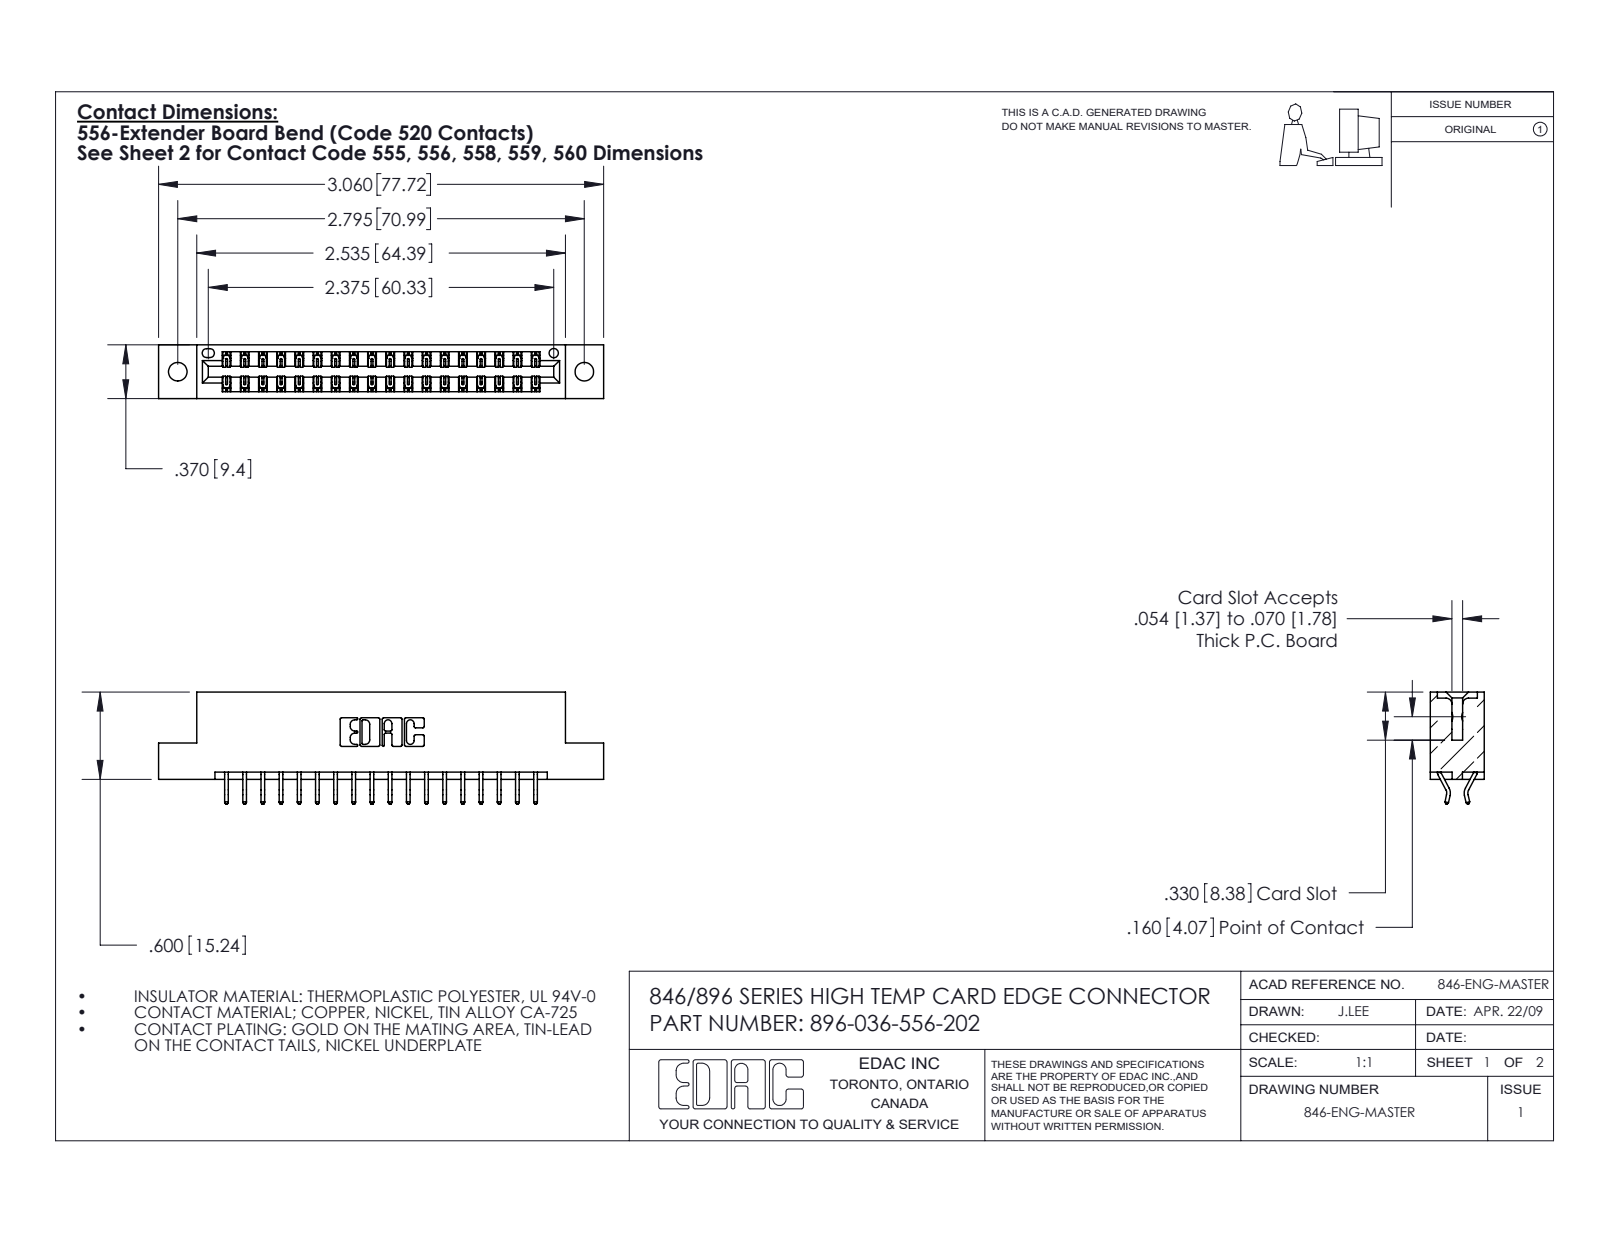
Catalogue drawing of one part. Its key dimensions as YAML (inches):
part_name: "396-036-556-202; 346 Part_Flush Mounting Lugs - 0.128 Dia; 345-292-001_556 Tail"
step_written_by: "SolidWorks 2016 (CONFIG_CONTROL_DESIGN)"
units: inches
bodies: {solids: 37, faces: 2210, planar: 1480, cylindrical: 730, other: 0}
overall_size: [3.06, 0.77, 0.37]
volume: 0.449
surface_area: 14.62
round_holes:
  - {diameter: 0.128, count: 2}
  - {diameter: 0.064, count: 1}
partial_cylinders:
  - {radius: 0.006, count: 54}
  - {radius: 0.01, count: 22}
  - {radius: 0.007, count: 6}
  - {radius: 0.031, count: 6}
  - {radius: 0.026, count: 3}
  - {radius: 0.01, count: 2}
  - {radius: 0.014, count: 2}
  - {radius: 0.022, count: 2}
face_to_face_distances: [0.048, 0.322, 0.25, 0.37, 0.025, 0.072, 0.298, 0.275, 0.148, 0.222]
hole_center_spacings: [0.246, 2.588, 2.795]
